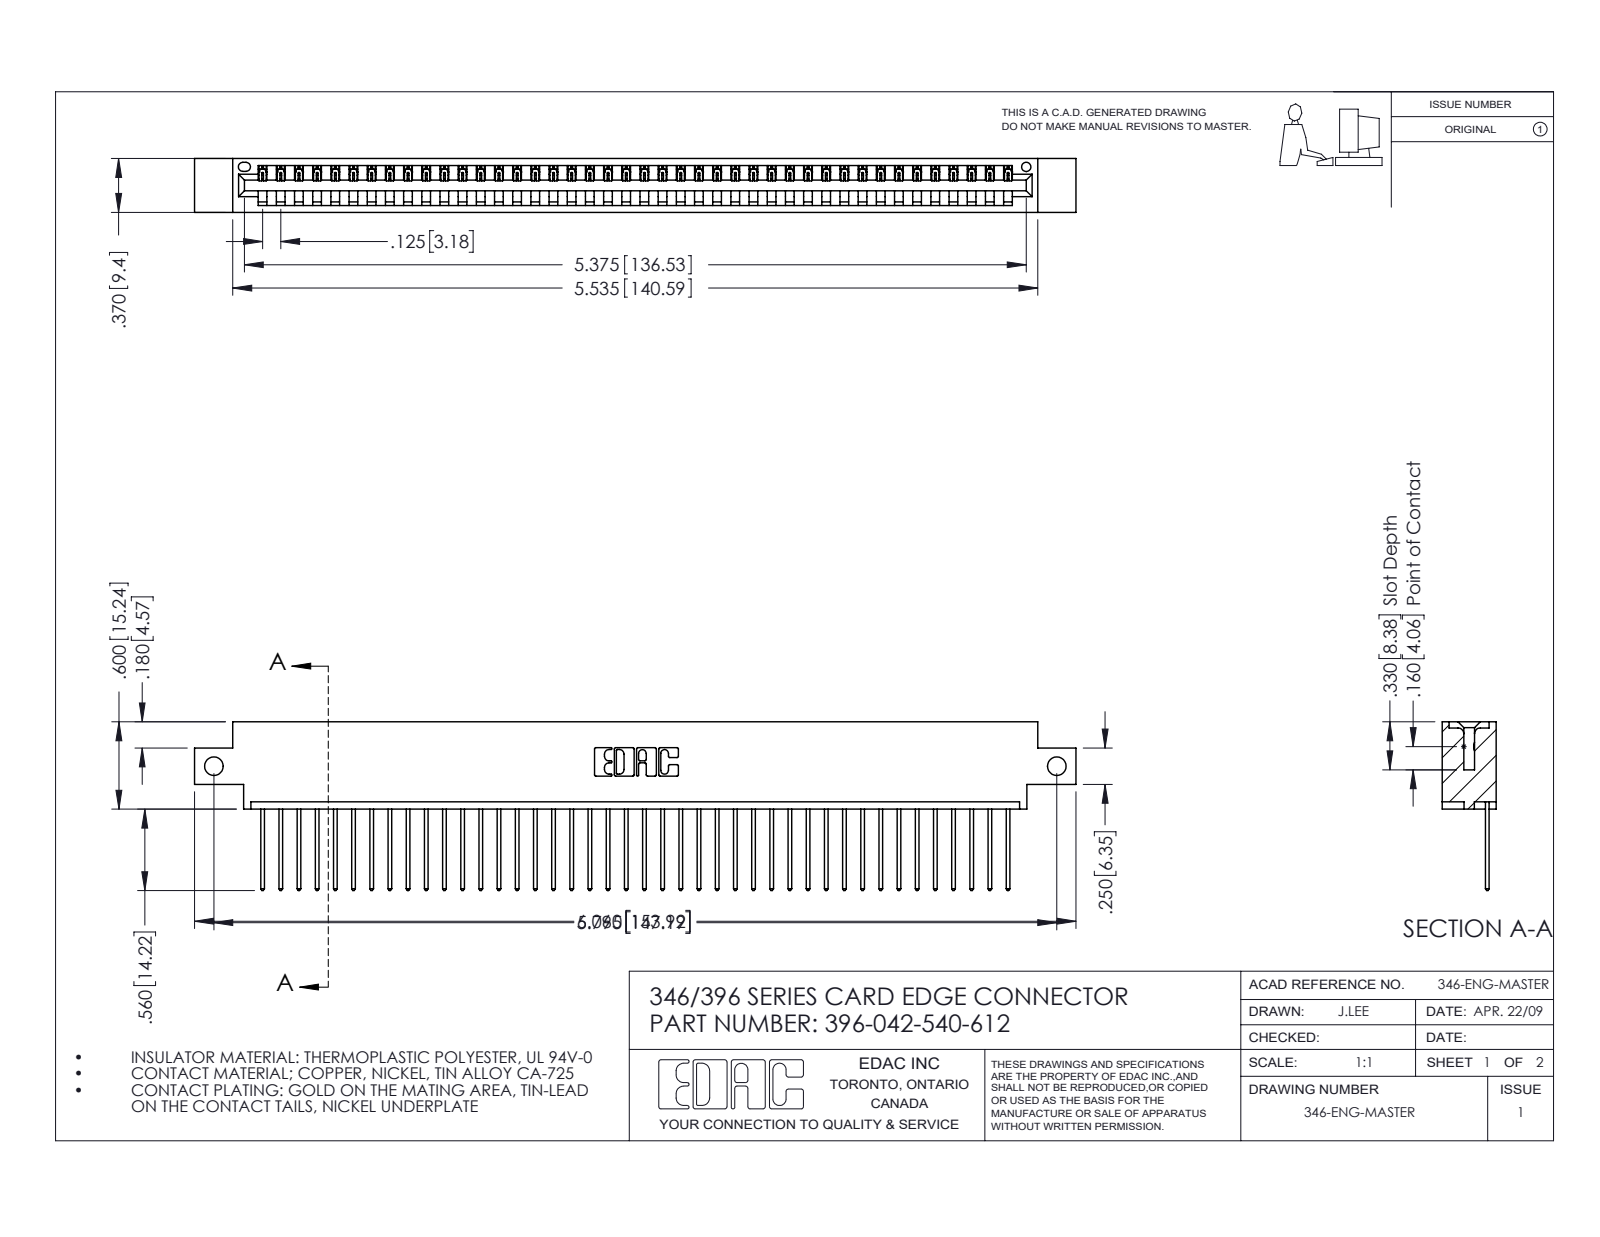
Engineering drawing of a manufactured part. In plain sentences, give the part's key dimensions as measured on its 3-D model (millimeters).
The part is named "346 Part_0.170 Offset - Side Mount; 345-292-001_345-293-140; 396-042-540-612". Its 3-D file was written by "SolidWorks 2016 (CONFIG_CONTROL_DESIGN)". It is 43 solids with 2562 faces: 1760 planar, 802 cylindrical and 0 other. Overall it measures 153.9 by 29.5 by 9.4 millimeters. Its volume is 14 600 cubic millimeters and its surface area 18 610 square millimeters. Round holes: 2 of diameter 3.3, 1 of diameter 1.6. Partial cylindrical surfaces (rounded edges, fillets, slot ends): 84 of radius 0.2, 84 of radius 0.3, 22 of radius 0.3, 6 of radius 0.2, 6 of radius 0.8, 3 of radius 0.7, 2 of radius 0.8, 2 of radius 1. The main face-to-face distances are 1.2, 8.2, 9.4, 6.4, 1.8, 7.6, 0.6, 3.8, 5.6, 2.5. The hole center spacings are 147.2.
